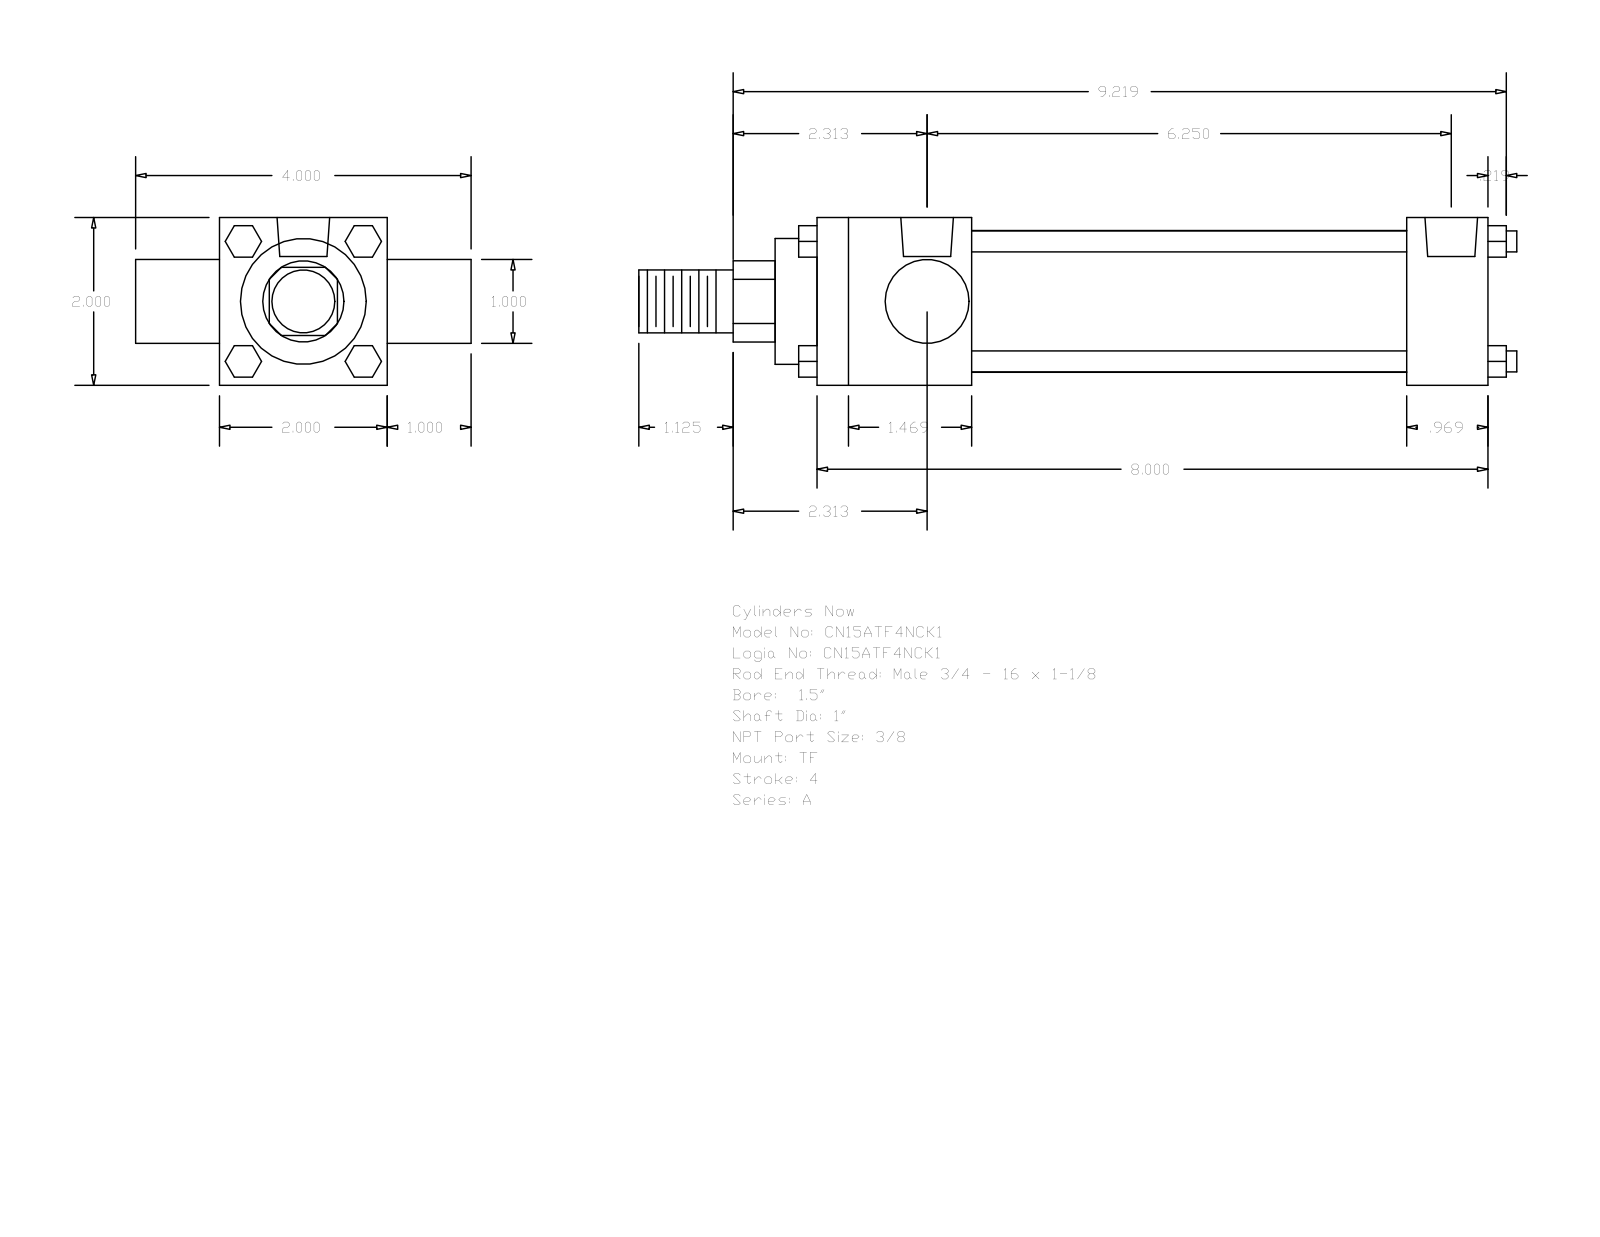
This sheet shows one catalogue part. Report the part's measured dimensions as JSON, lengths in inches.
{"part_name": "A_TF__0150_1", "step_written_by": "GSSL Pune (CONFIG_CONTROL_DESIGN)", "units": "inches", "bodies": {"solids": 0, "faces": 120, "planar": 92, "cylindrical": 28, "other": 0}, "overall_size": [10.469, 4, 2], "round_holes": [[0.219, 3], [0.627, 2]], "round_bosses_or_shafts": [[0.25, 4], [1, 2], [1.69, 1], [1.5, 1], [0.75, 1]], "partial_cylinders_radius": [[0.484, 1]], "face_to_face_distances": [2, 1, 8, 3, 1.844, 7.031, 5.187, 6.156, 0.969, 0.5], "hole_center_spacings": [0.156, 6.094, 5.937, 6.25]}
